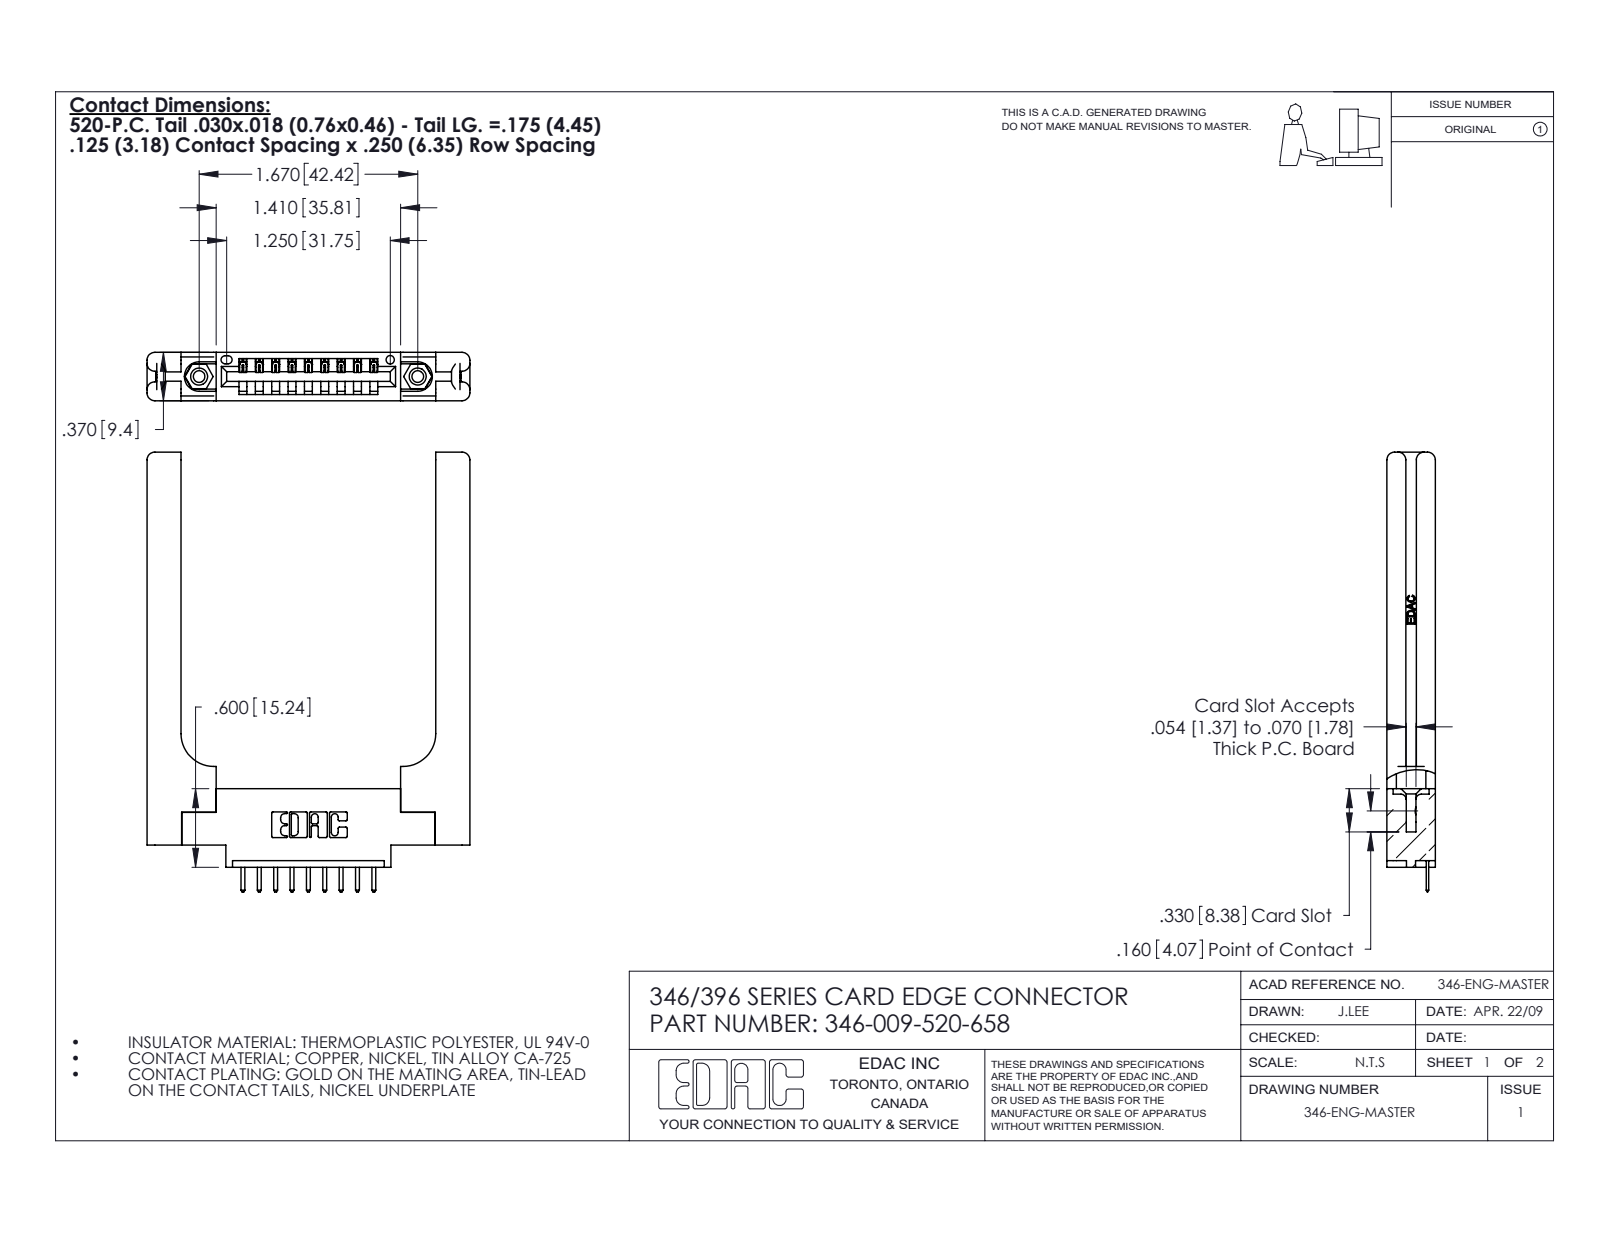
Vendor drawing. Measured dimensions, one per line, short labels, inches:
name: 345-292-001_345-293-120; 346-009-520-658; 345-250-001_345-250-001-102; 346-220-058_345-220-058 (+1 more)
written by: SolidWorks 2020 (CONFIG_CONTROL_DESIGN)
unit: in
bodies: 14 solids, 954 faces (620 planar, 274 cylindrical, 60 other)
size: 3.358 × 2.466 × 0.37
volume: 0.799 in³; area: 18.42 in²
holes: 2× ⌀0.089, 2× ⌀0.125, 2× ⌀0.156, 1× ⌀0.064
bosses: 2× ⌀0.155
rounds: 22× R0.01, 20× R0.01, 18× R0.006, 16× R0.06, 6× R0.007, 6× R0.031, 3× R0.026, 2× R0.03
face distances: 0.37, 0.15, 0.22, 0.072, 0.148, 0.25, 0.102, 0.048, 0.322, 0.173
hole spacings: 0.246, 1.465, 1.67
